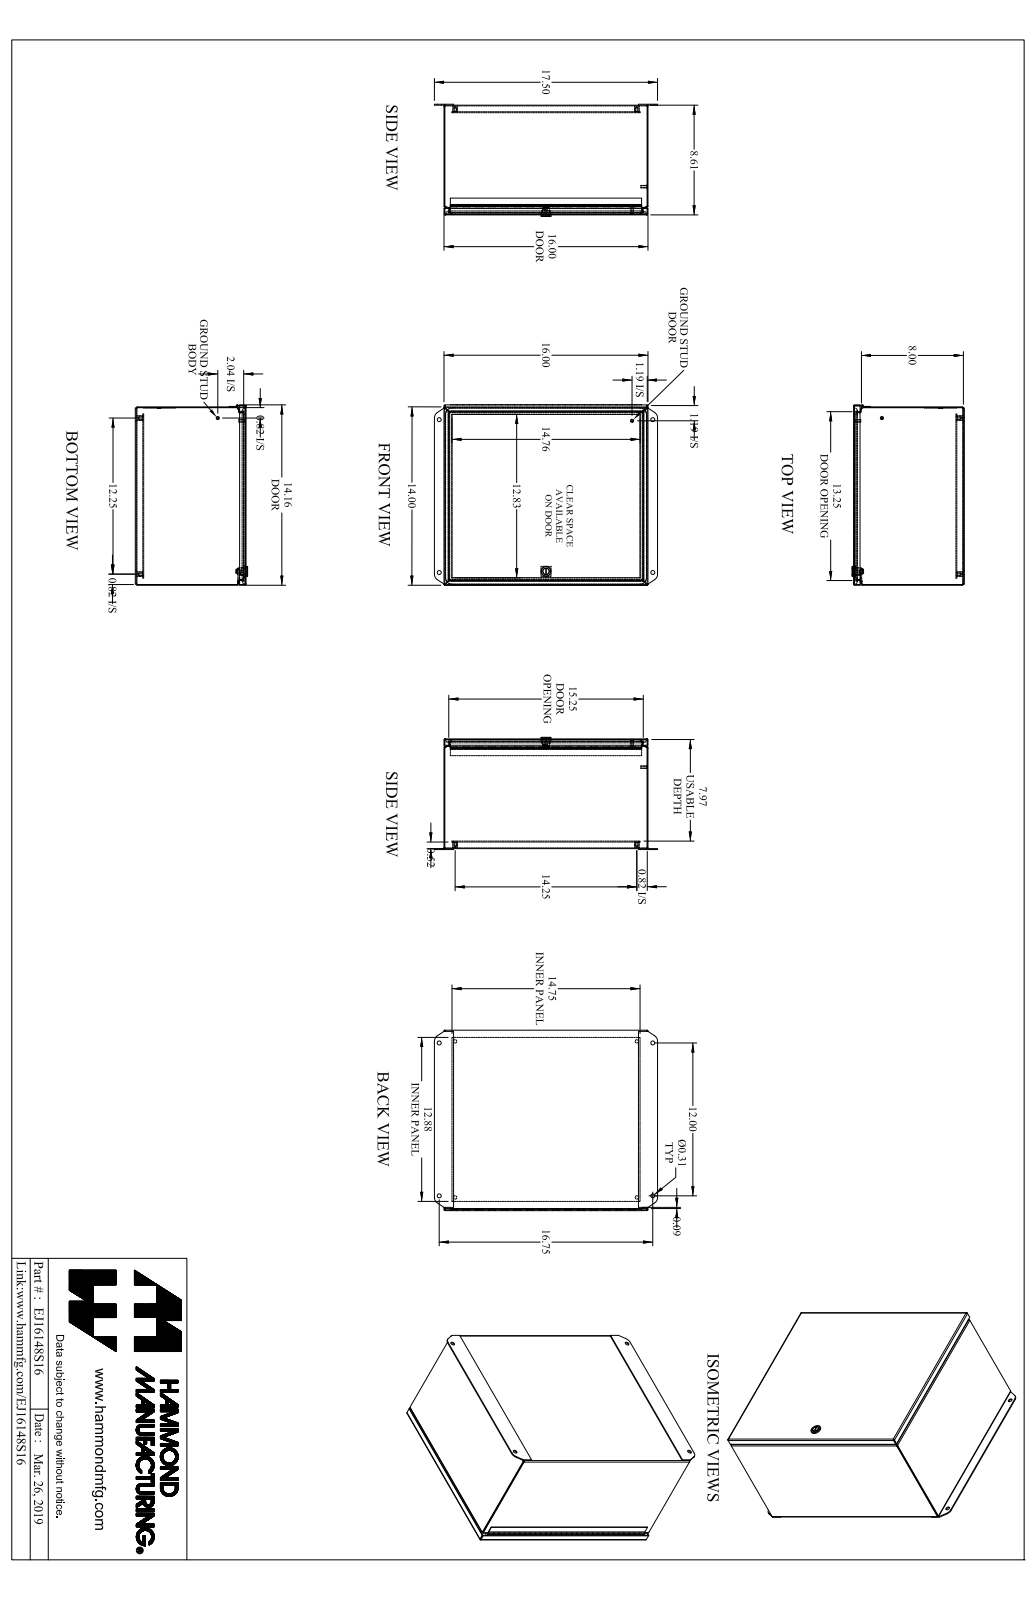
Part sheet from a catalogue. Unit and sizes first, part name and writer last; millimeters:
Units: millimetres
Overall size (bounding box): 444.5 × 359.8 × 223.6
Round holes (diameter × count): ⌀4 ×4, ⌀6.7 ×4, ⌀8 ×4, ⌀1.3 ×1, ⌀13.1 ×1
Round bosses / shafts (diameter × count): ⌀9.5 ×4, ⌀6.4 ×2, ⌀4.8 ×2, ⌀20 ×1, ⌀13.6 ×1, ⌀12.6 ×1, ⌀11 ×1, ⌀2.5 ×1
Partial cylindrical surfaces — rounded edges, fillets, slot ends (radius × count): R0.7 ×16, R2.2 ×16, R7.1 ×12, R6.4 ×4, R12.7 ×4, R12.7 ×4, R1.5 ×2, R0.8 ×1
Main face-to-face distances: 1.4, 217.3, 354.2, 1.8, 15, 405, 218.7, 215.8, 205.6, 204.1
Hole centre spacings: 31.9, 309.6, 393.7, 499.8, 181.1, 212.8, 304.8, 311.2
Volume: 1 305 000 mm³ · Surface area: 1 703 000 mm²
Bodies: 16 solids, 692 faces (358 planar, 254 cylindrical, 80 other)
Part name (STEP PRODUCT): EJ16148S16_Default
STEP written by: SolidWorks 2019 (CONFIG_CONTROL_DESIGN)
